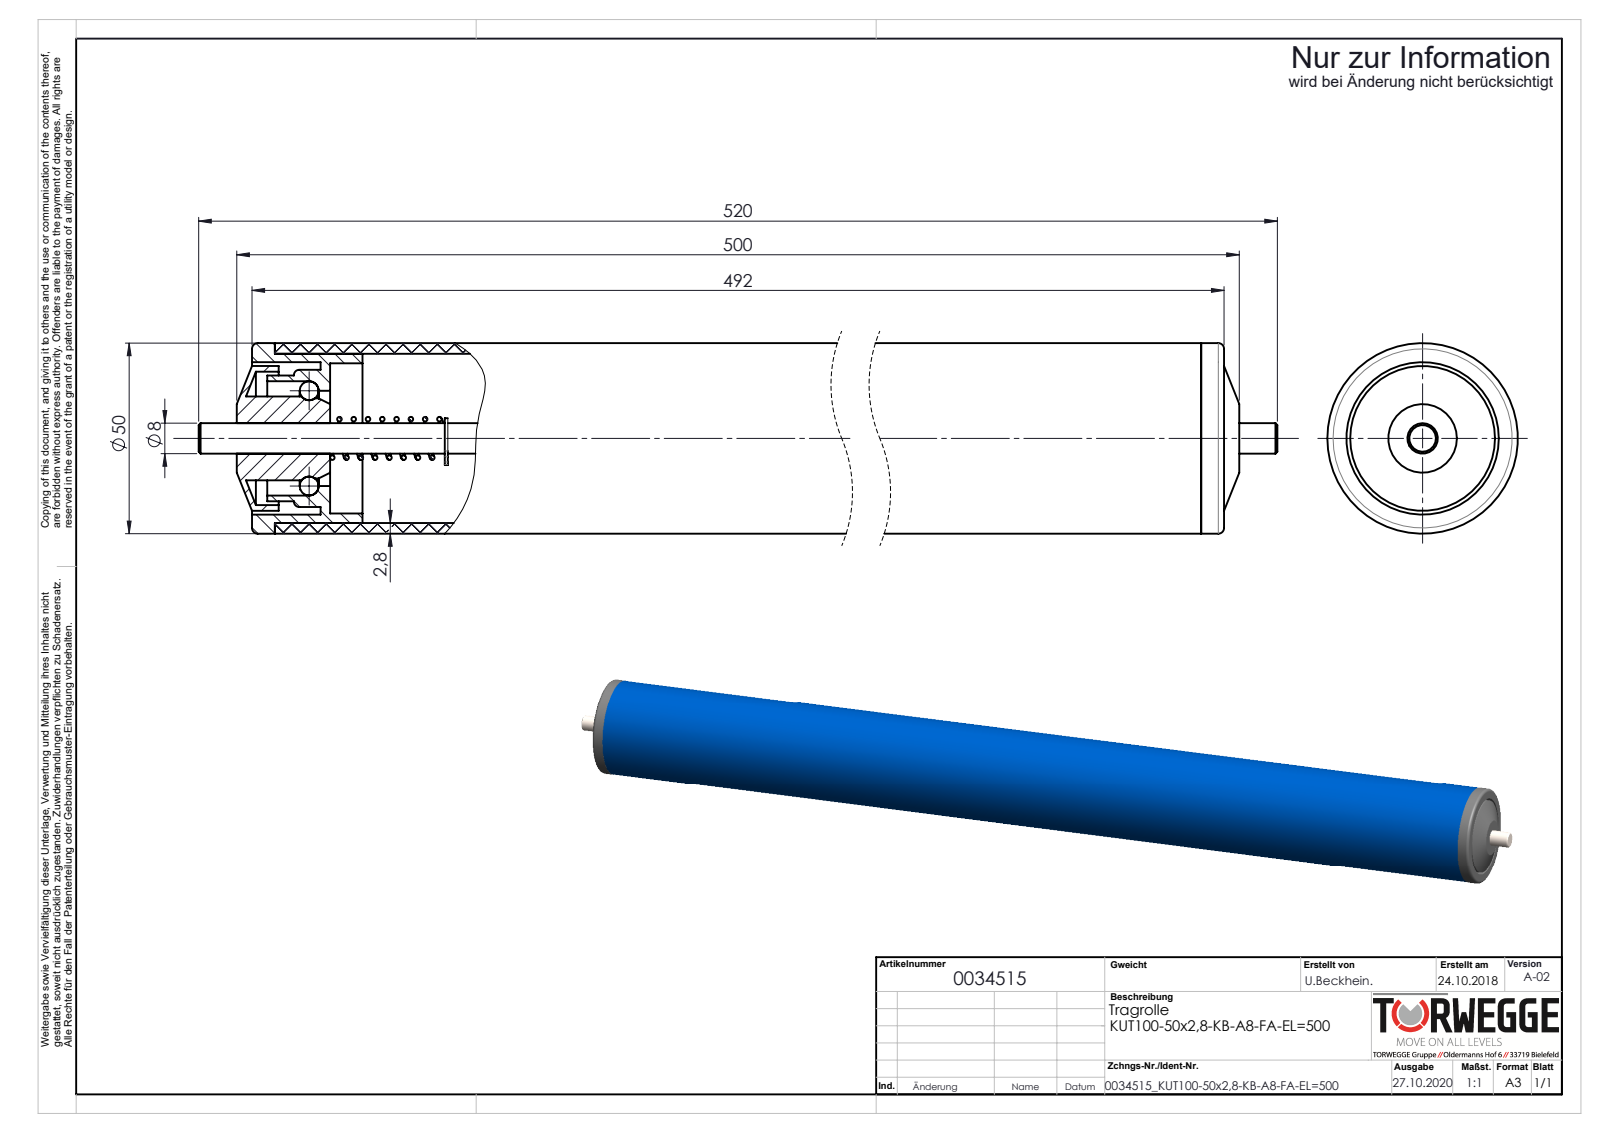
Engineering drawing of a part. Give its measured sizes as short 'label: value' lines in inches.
name: 0034515
written by: SolidWorks 2018 (AUTOMOTIVE_DESIGN)
unit: in
bodies: 11 solids, 186 faces (52 planar, 88 cylindrical, 46 other)
size: 20.472 × 1.969 × 1.969
volume: 17.17 in³; area: 306.8 in²
holes: 1× ⌀0.299, 1× ⌀0.315, 1× ⌀0.984, 1× ⌀1.181, 1× ⌀1.378, 1× ⌀1.551, 1× ⌀1.575
bosses: 1× ⌀1.969, 1× ⌀1.748, 1× ⌀1.496, 1× ⌀1.417, 1× ⌀1.299, 1× ⌀0.866, 1× ⌀0.827
rounds: 2× R0.024, 2× R0.03, 2× R0.096, 1× R0.192, 1× R0.276
face distances: 0.571, 18.327, 0.433, 0.236, 0.807, 18.563, 19.134, 17.756, 18.898, 19.37
